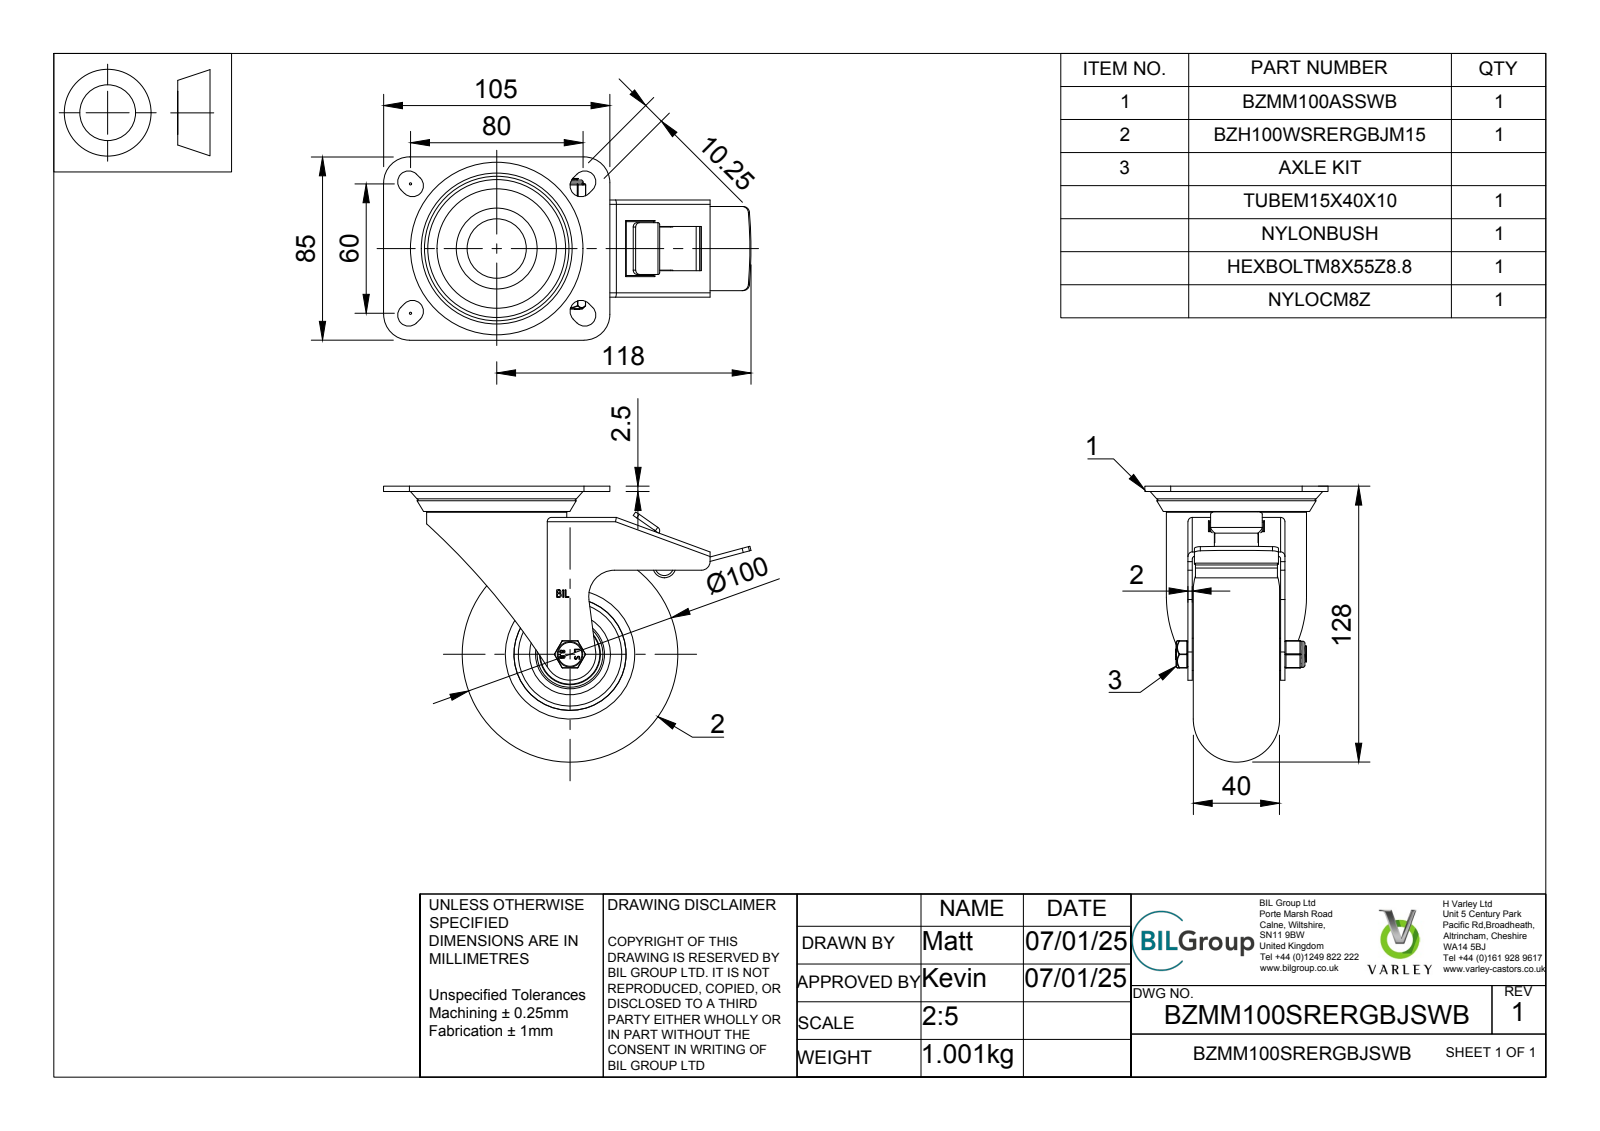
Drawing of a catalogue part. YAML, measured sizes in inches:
part_name: "BZMM100SRERGBJSWB v3; BZH100WSRERGBJM15 v1; 55 SHORE A ELASTIC RUBBER; ALUMINIUM RIM (+8 more)"
step_written_by: "Autodesk Translation Framework v13.20.0.188 (AP242_MANAGED_MODEL_BASED_3D_ENGINEERING_MIM_LF)"
units: inches
bodies: {solids: 65, faces: 1306, planar: 531, cylindrical: 237, other: 538}
overall_size: [6.713, 5.039, 3.346]
volume: 19.39
surface_area: 210.7
round_holes:
  - {diameter: 0.026, count: 2}
  - {diameter: 0.315, count: 1}
  - {diameter: 0.323, count: 1}
  - {diameter: 0.339, count: 1}
  - {diameter: 0.402, count: 1}
  - {diameter: 0.591, count: 1}
  - {diameter: 0.807, count: 1}
  - {diameter: 1.024, count: 1}
  - {diameter: 1.055, count: 1}
  - {diameter: 1.083, count: 1}
  - {diameter: 1.102, count: 1}
  - {diameter: 1.11, count: 1}
round_bosses_or_shafts:
  - {diameter: 2.559, count: 1}
  - {diameter: 1.476, count: 1}
  - {diameter: 1.24, count: 1}
  - {diameter: 0.846, count: 1}
  - {diameter: 0.787, count: 1}
  - {diameter: 0.748, count: 1}
  - {diameter: 0.589, count: 1}
  - {diameter: 0.476, count: 1}
partial_cylinders:
  - {radius: 0.02, count: 22}
  - {radius: 0.01, count: 12}
  - {radius: 0.079, count: 9}
  - {radius: 0.202, count: 8}
  - {radius: 0.039, count: 6}
  - {radius: 0.472, count: 5}
  - {radius: 0.013, count: 4}
  - {radius: 0.025, count: 4}
face_to_face_distances: [0.079, 0.098, 0.02, 1.693, 1.594, 1.673, 0.039, 1.614, 1.772, 0.571]
hole_center_spacings: [0.127, 0.098]
